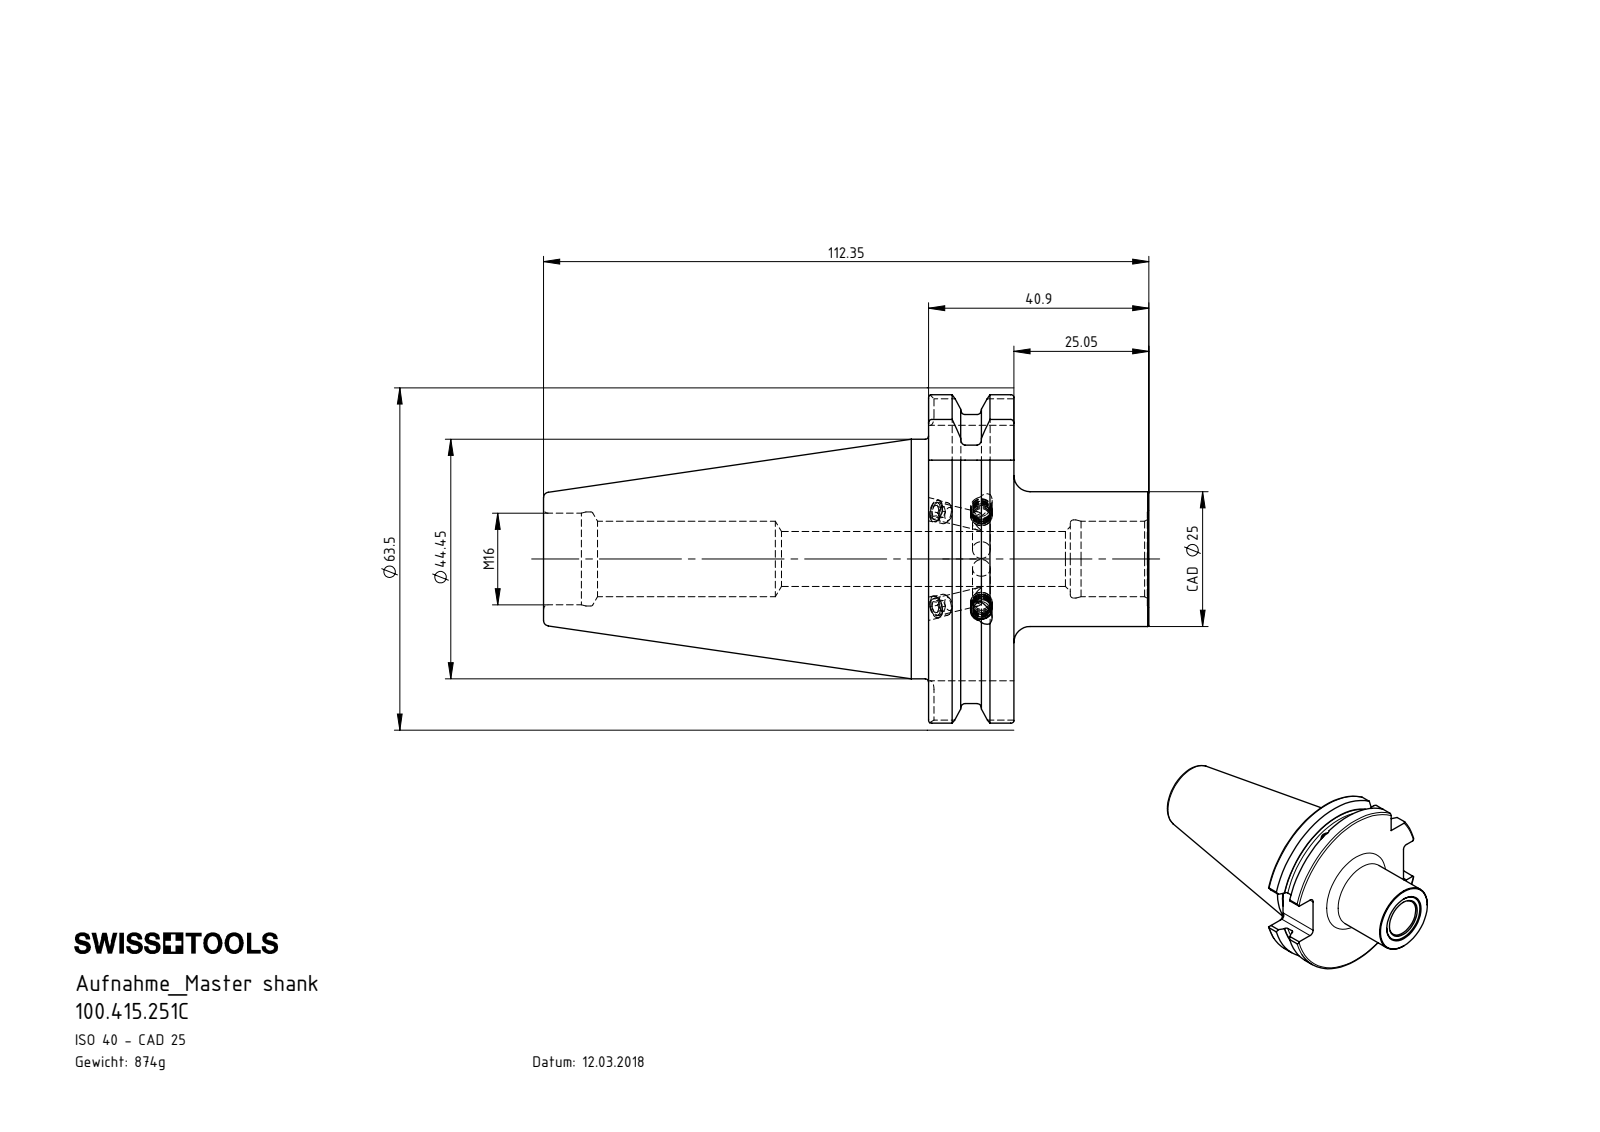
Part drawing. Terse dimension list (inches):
name: SB4.CA2.K01.044; SK4-CA2.K01.044_B; KVT_MB_600_040; ISO 4026 - M4 x 3_PreviewCfg
written by: SolidWorks 2017 (AUTOMOTIVE_DESIGN)
unit: in
bodies: 7 solids, 169 faces (57 planar, 41 cylindrical, 71 other)
size: 4.423 × 2.5 × 2.399
volume: 6.791 in³; area: 36.51 in²
holes: 3× ⌀0.13, 2× ⌀0.118, 2× ⌀0.165, 1× ⌀0.157, 1× ⌀0.402, 1× ⌀0.551, 1× ⌀0.571, 1× ⌀0.669, 1× ⌀0.687
bosses: 4× ⌀0.157, 1× ⌀1.75, 1× ⌀0.984
rounds: 8× R0.063, 1× R1.102, 1× R1.25
face distances: 0.624, 1.61, 0.986, 1.866, 2.813, 3.437, 4.423, 0.634, 1.039, 0.406
